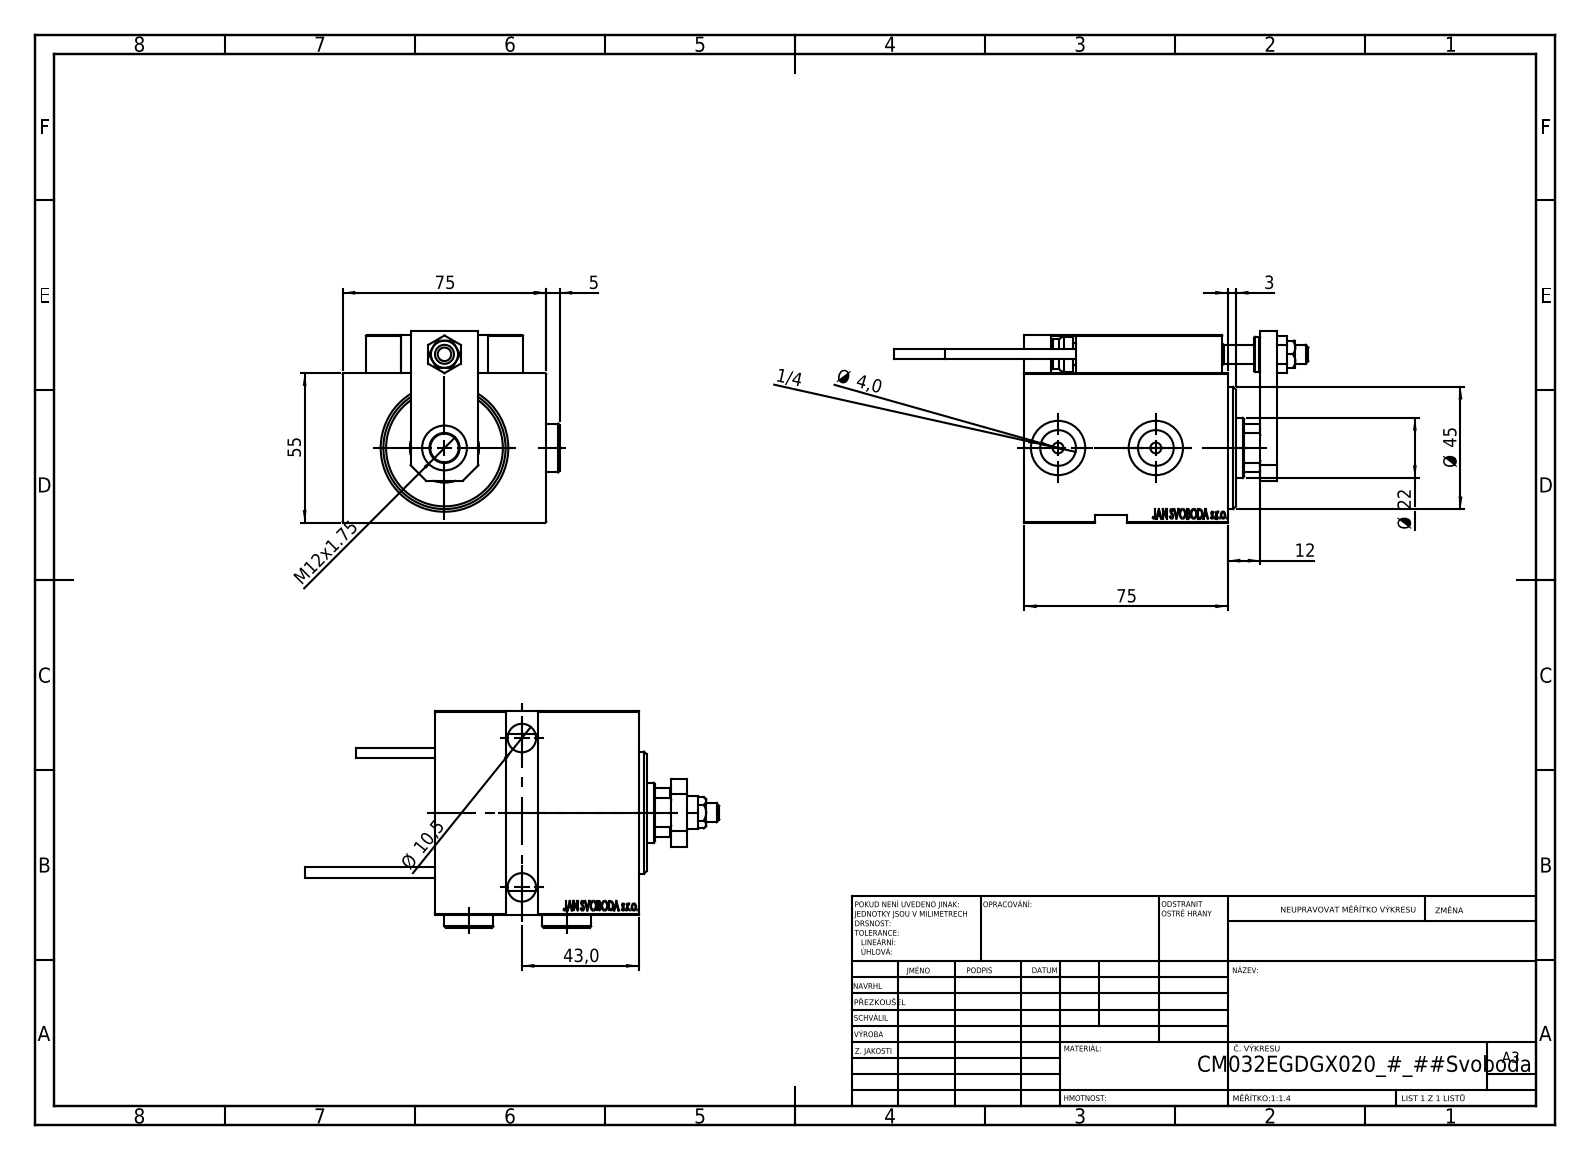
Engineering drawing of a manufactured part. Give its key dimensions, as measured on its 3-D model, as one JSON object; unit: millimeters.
{"part_name": "MAGNET; ZARAZKA; NUT_D12; SWITCH_X_FRONT_BACK (+7 more)", "step_written_by": "SolidWorks 2019 (CONFIG_CONTROL_DESIGN)", "units": "millimeters", "bodies": {"solids": 26, "faces": 1336, "planar": 603, "cylindrical": 188, "other": 545}, "overall_size": [152.7, 79.9, 70.5], "volume_mm3": 332434, "surface_area_mm2": 80389, "round_holes": [[4, 6], [8, 5], [3.2, 4], [10.5, 3], [16.5, 3], [5, 2], [13.16, 2], [20, 2], [7, 1], [22, 1], [25.5, 1], [32, 1]], "round_bosses_or_shafts": [[18, 2], [5, 2], [3.8, 2], [34, 1], [13, 1], [11, 1]], "partial_cylinders_radius": [[0.3, 30], [3, 2], [10.5, 1]], "face_to_face_distances": [75, 55, 12, 3, 10, 14, 5, 25, 65, 7], "hole_center_spacings": [11.37, 20, 27.07, 29.59, 29.69, 32.18, 34.83, 36.06]}
